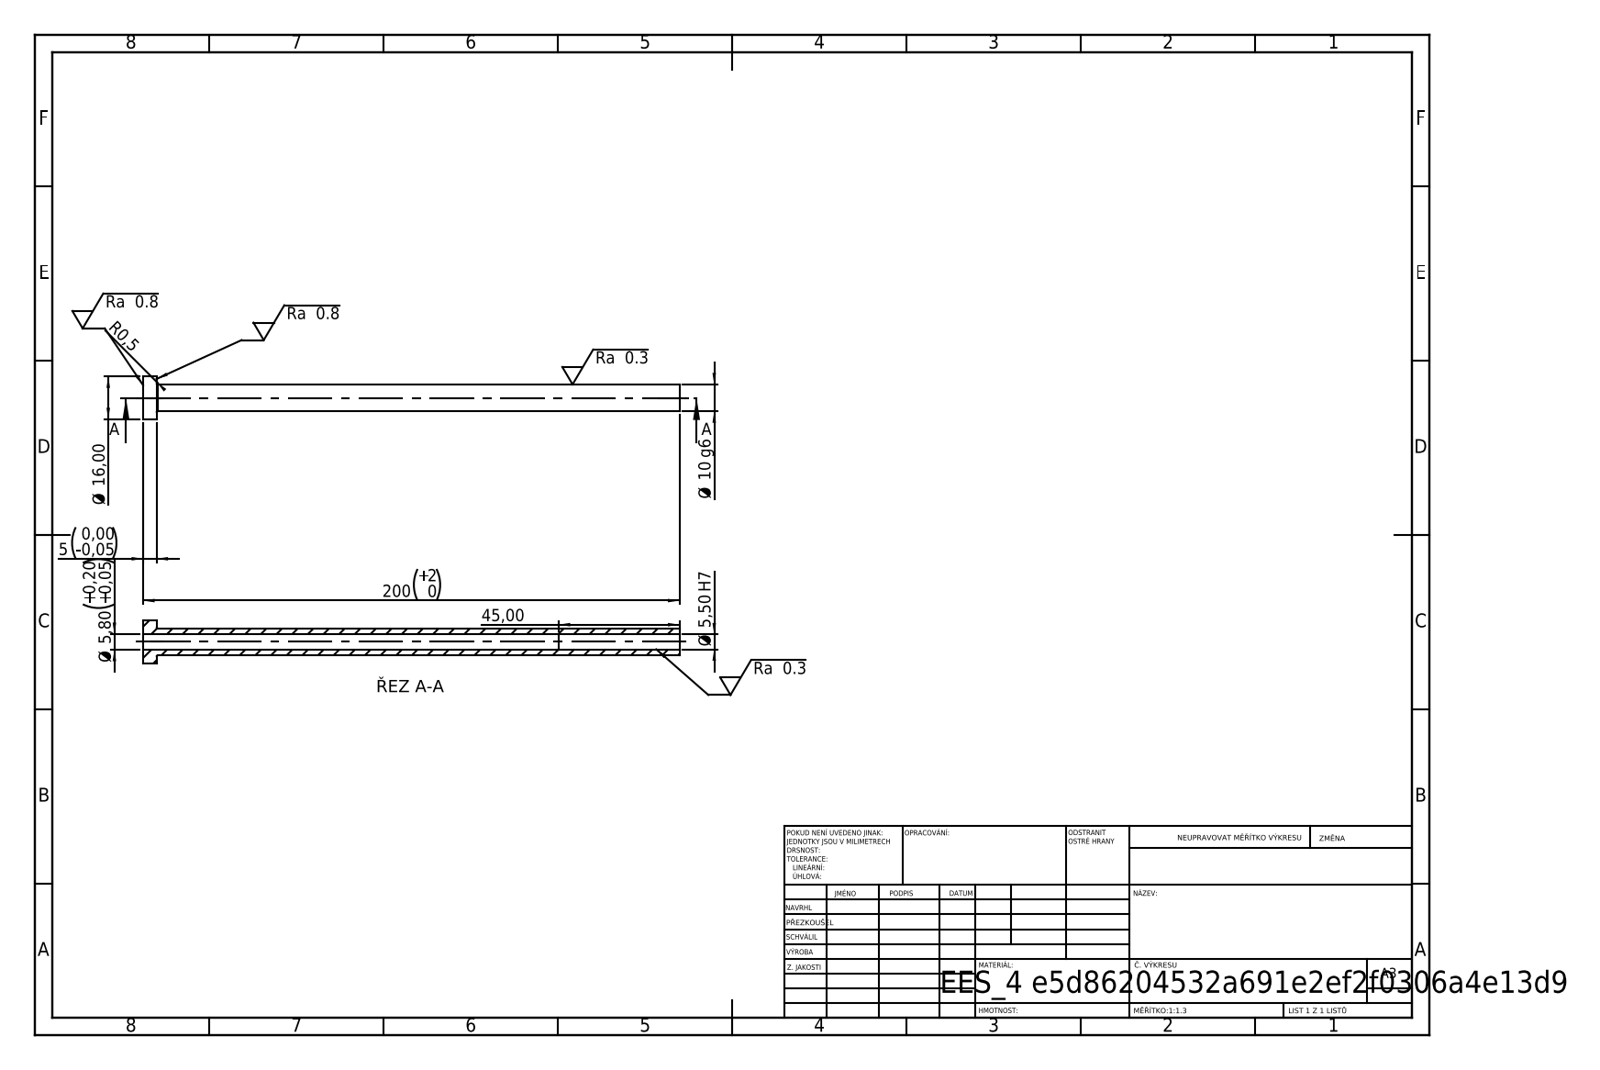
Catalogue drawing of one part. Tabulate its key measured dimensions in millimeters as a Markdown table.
| quantity | value |
| --- | --- |
| STEP written by | SolidWorks 2019 (CONFIG_CONTROL_DESIGN) |
| units | millimeters |
| bodies | 1 solid, 14 faces (4 planar, 8 cylindrical, 2 other) |
| overall size | 200 × 16 × 16 |
| volume | 11 158 mm³ |
| surface area | 10 327 mm² |
| round holes (diameter × count) | 5.5 × 1, 5.8 × 1 |
| round bosses / shafts (diameter × count) | 16 × 1, 10 × 1 |
| main face-to-face distances | 5, 200, 195, 155, 150, 45 |
